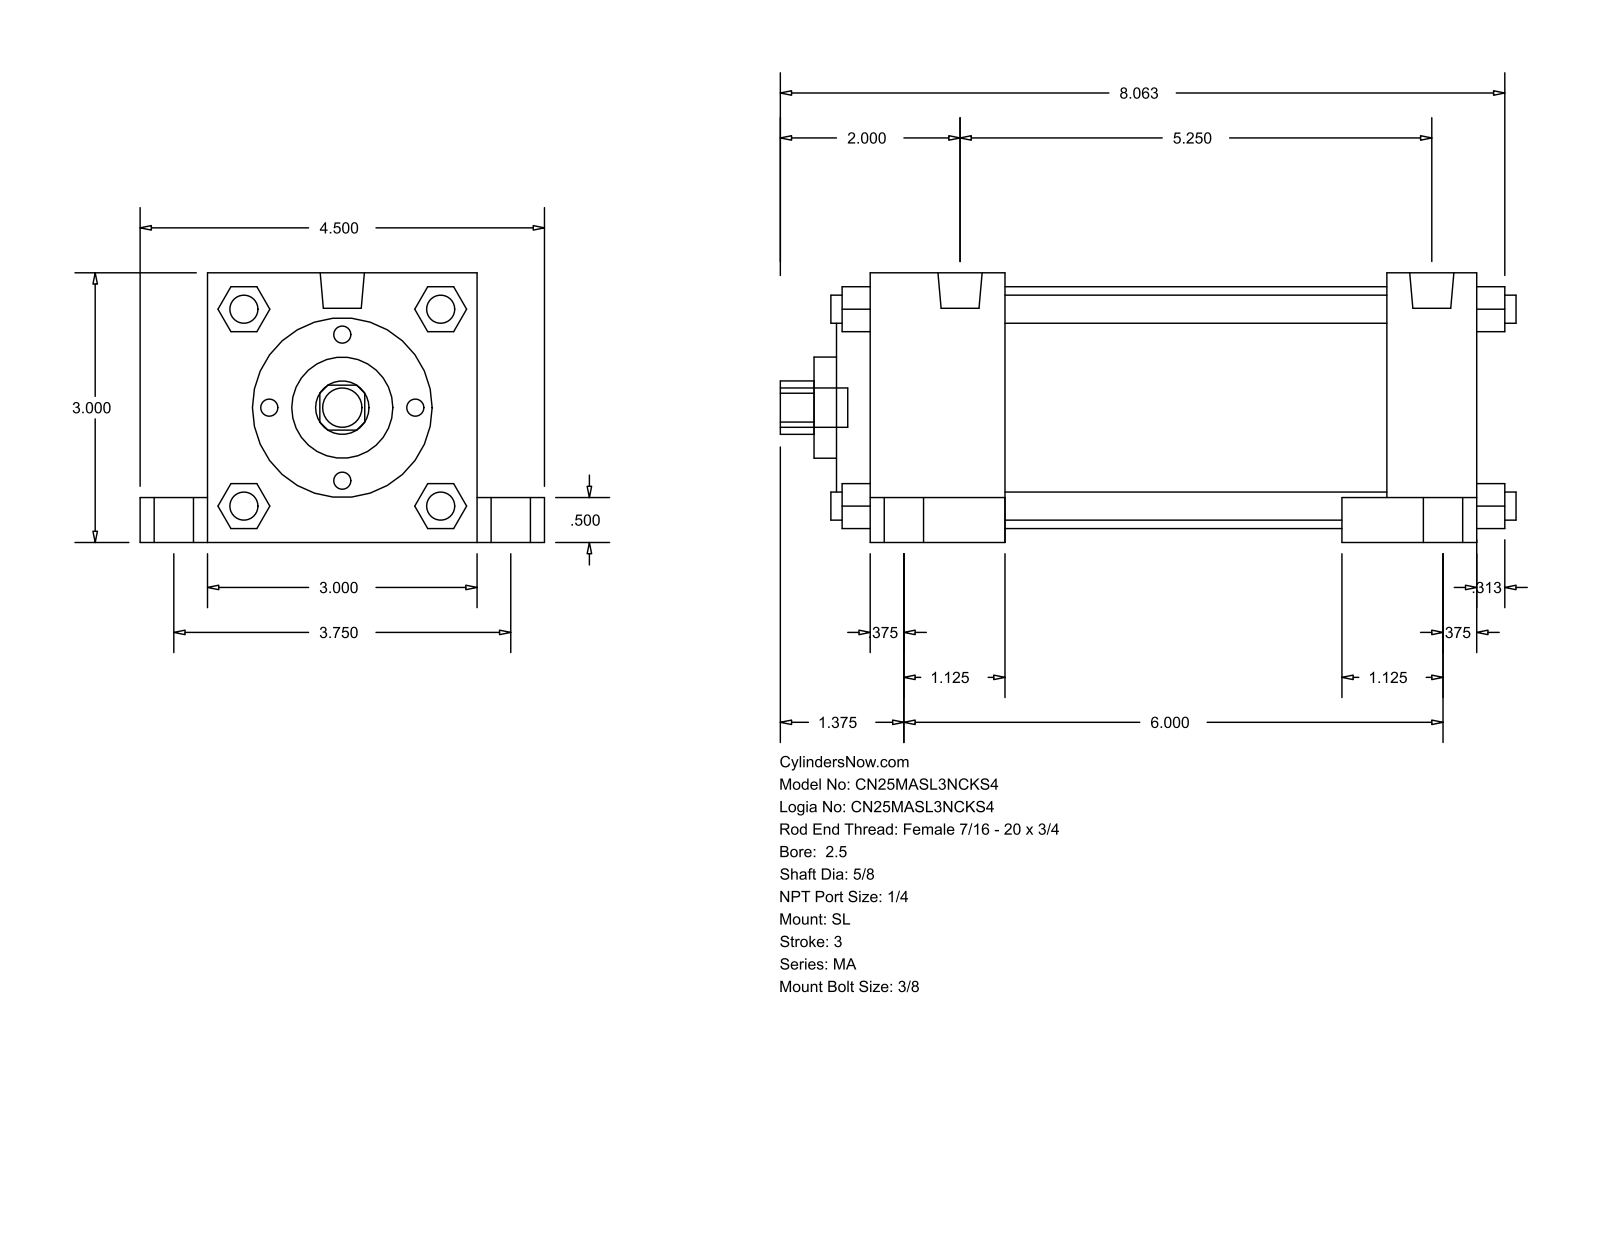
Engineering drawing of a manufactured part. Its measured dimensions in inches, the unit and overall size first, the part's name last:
Units: inches
Overall size (bounding box): 8.187 × 4.5 × 3
Round holes (diameter × count): ⌀0.625 ×1, ⌀1.125 ×1, ⌀2 ×1, ⌀2.69 ×1
Round bosses / shafts (diameter × count): ⌀0.313 ×8, ⌀0.437 ×5, ⌀0.687 ×4, ⌀0.492 ×2
Partial cylindrical surfaces — rounded edges, fillets, slot ends (radius × count): R0.297 ×1
Main face-to-face distances: 3, 6.75, 0.5, 4.25, 1, 1.5, 5.25, 5.75, 0.75, 2.5
Bodies: 0 solids, 150 faces (113 planar, 37 cylindrical, 0 other)
Part name (STEP PRODUCT): MA_SL__0250_0.625
STEP written by: GSSL Pune (CONFIG_CONTROL_DESIGN)
